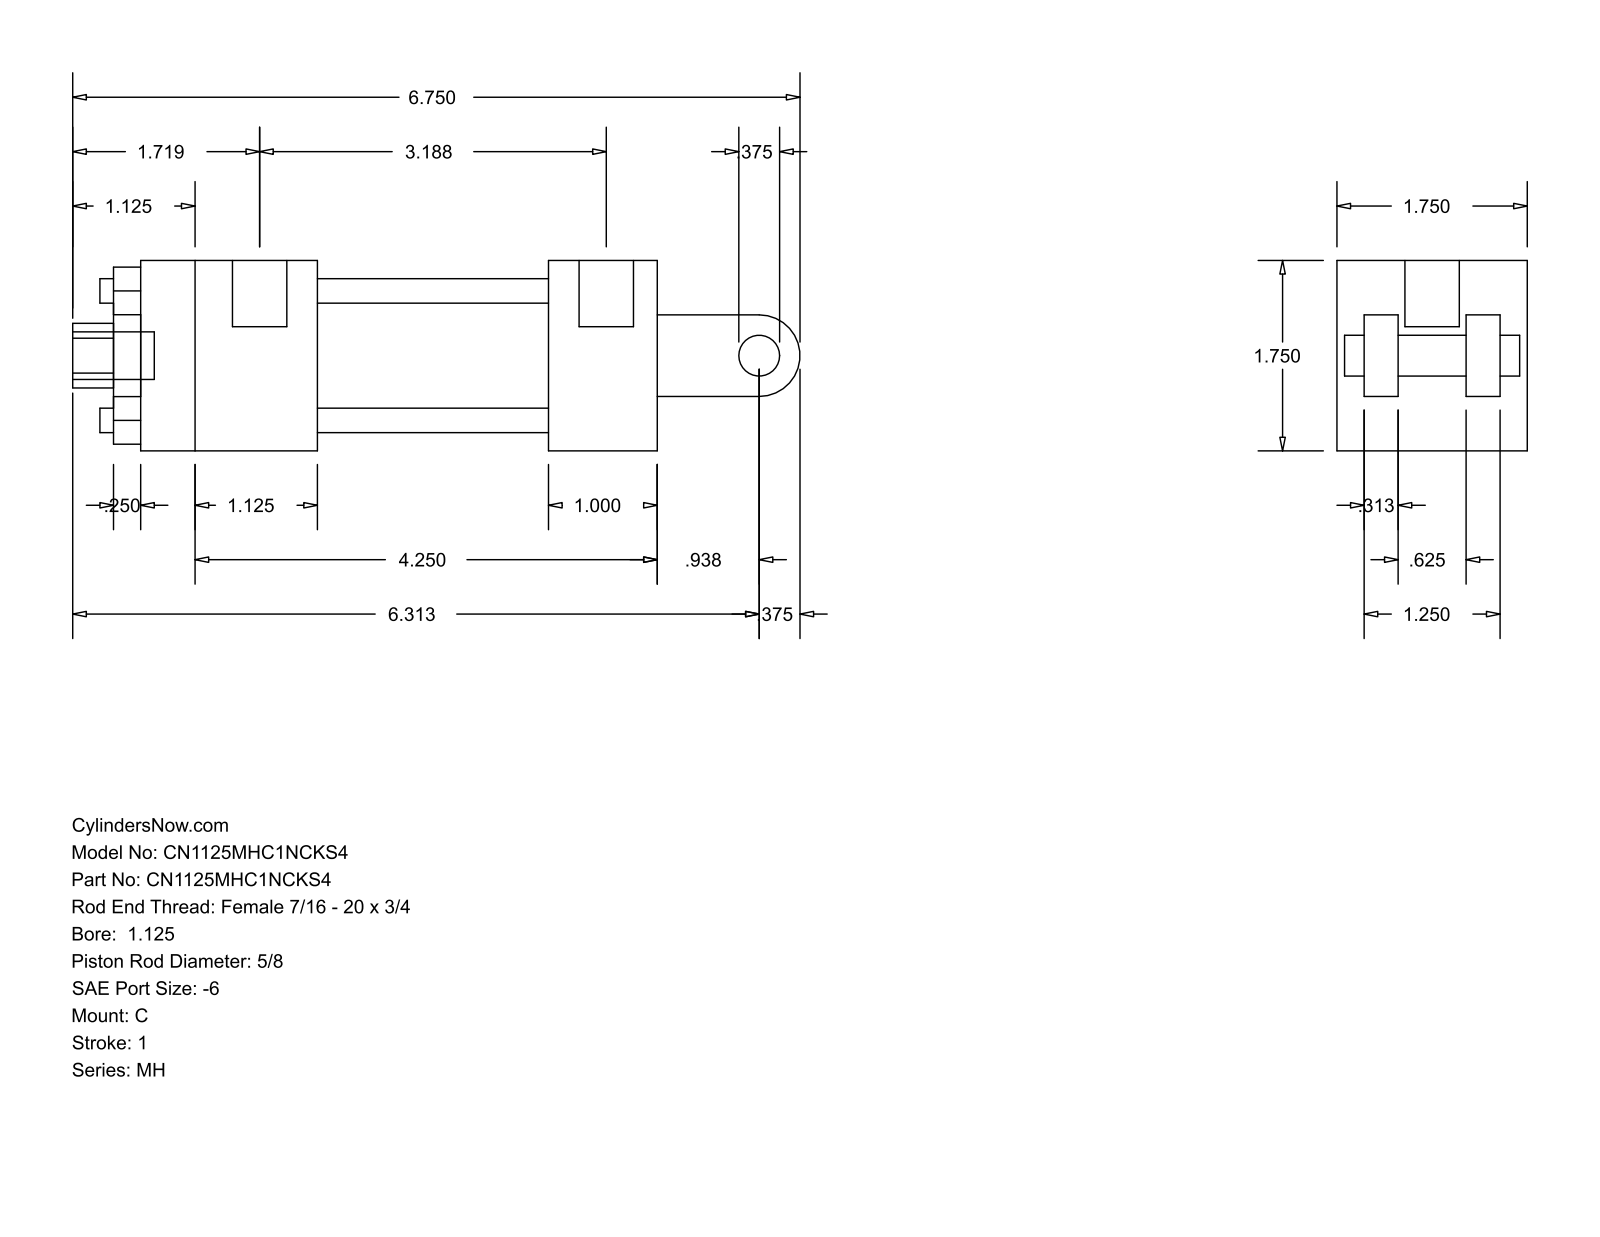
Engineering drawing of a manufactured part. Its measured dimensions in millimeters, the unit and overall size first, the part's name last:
Units: millimetres
Overall size (bounding box): 169.86 × 44.45 × 44.45
Round holes (diameter × count): ⌀5.71 ×4, ⌀5.56 ×2, ⌀12.7 ×1, ⌀15.88 ×1, ⌀28.57 ×1, ⌀34.92 ×1
Round bosses / shafts (diameter × count): ⌀5.56 ×2, ⌀12.7 ×1, ⌀11.11 ×1, ⌀9.53 ×1
Partial cylindrical surfaces — rounded edges, fillets, slot ends (radius × count): R7.54 ×1, R9.53 ×1
Main face-to-face distances: 44.46, 6.35, 31.76, 14.29, 12.7, 30.17, 38.11, 7.94, 23.82, 41.27
Hole centre spacings: 21.37, 30.22, 42.74
Bodies: 0 solids, 99 faces (70 planar, 29 cylindrical, 0 other)
Part name (STEP PRODUCT): MH_C__0112_0.625
STEP written by: GSSL Pune (CONFIG_CONTROL_DESIGN)
